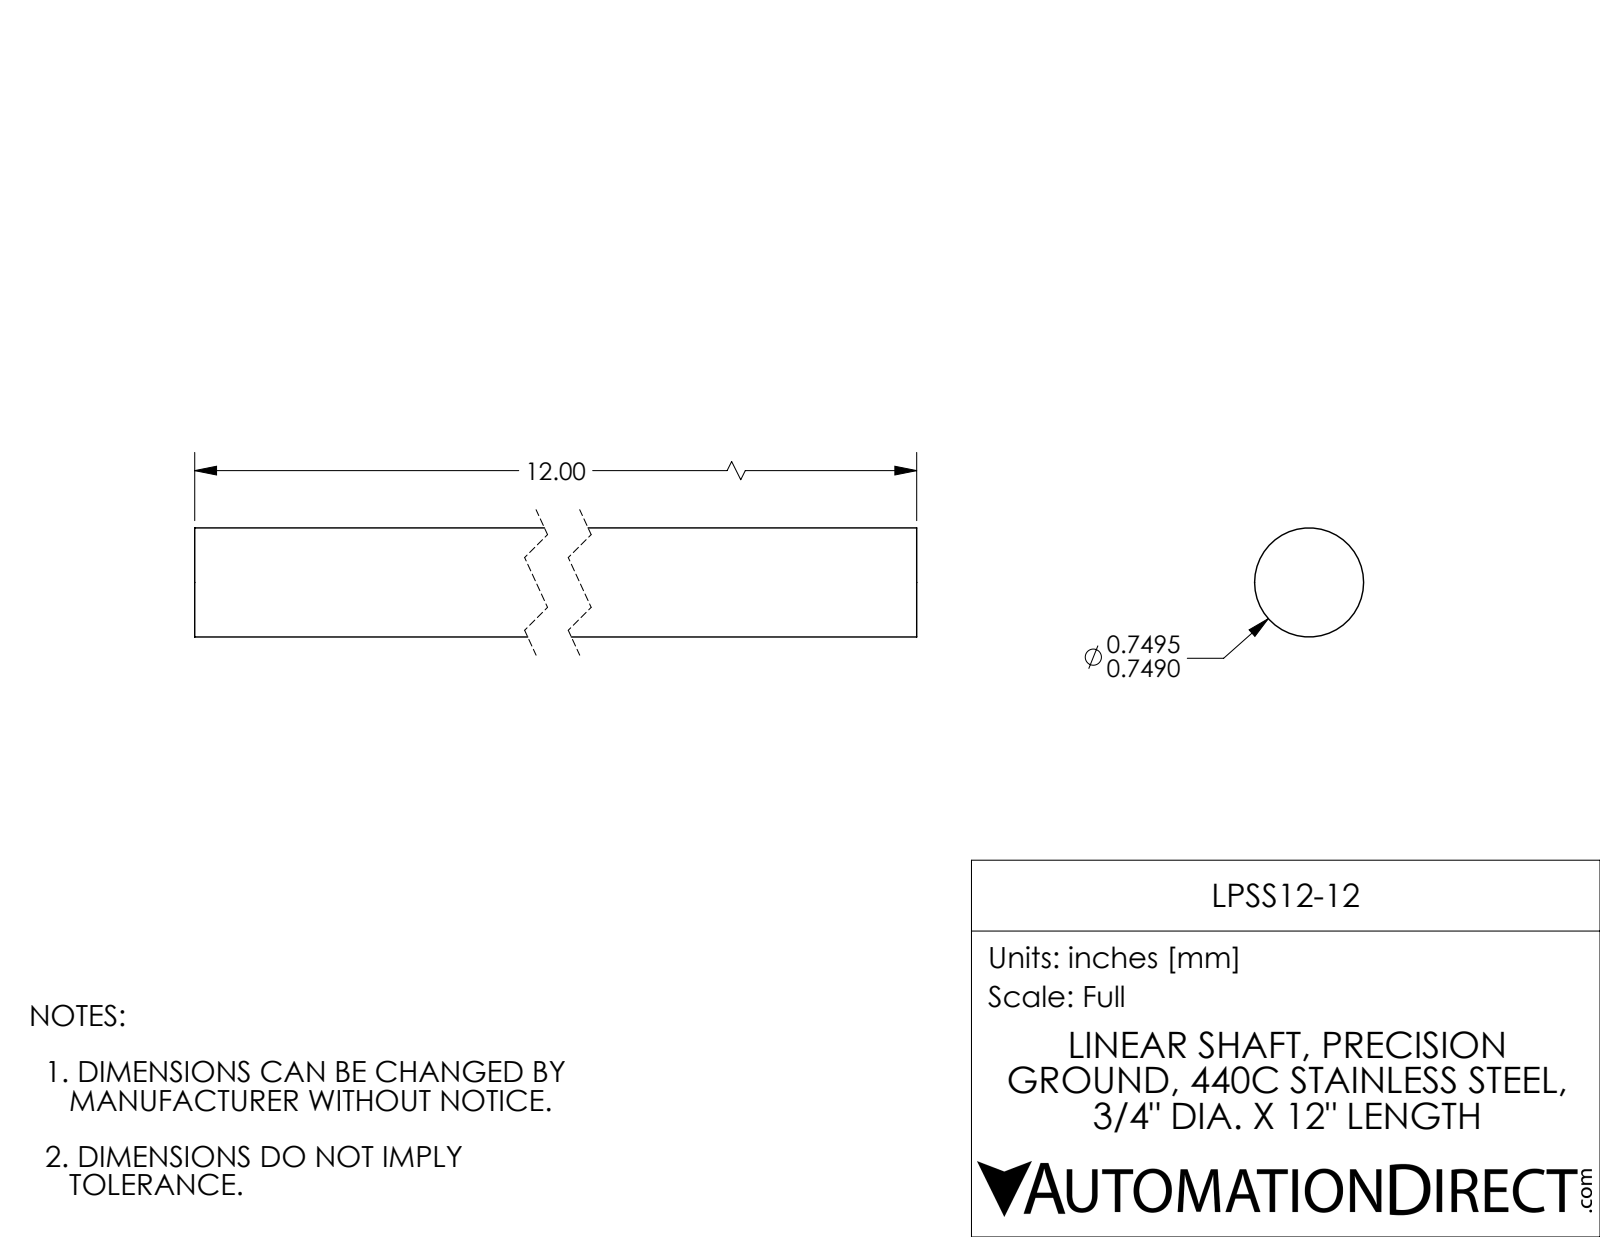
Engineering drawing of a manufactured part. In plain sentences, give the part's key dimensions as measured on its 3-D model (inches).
The part is named "LPSS12-12". Its 3-D file was written by "SolidWorks 2017 (AUTOMOTIVE_DESIGN)". It is 1 solid with 4 faces: 2 planar, 2 cylindrical and 0 other. Overall it measures 12 by 0.749 by 0.749 inches. Its volume is 5.294 cubic inches and its surface area 29.14 square inches. Round bosses or shafts: 1 of diameter 0.75. The main face-to-face distances are 12.
